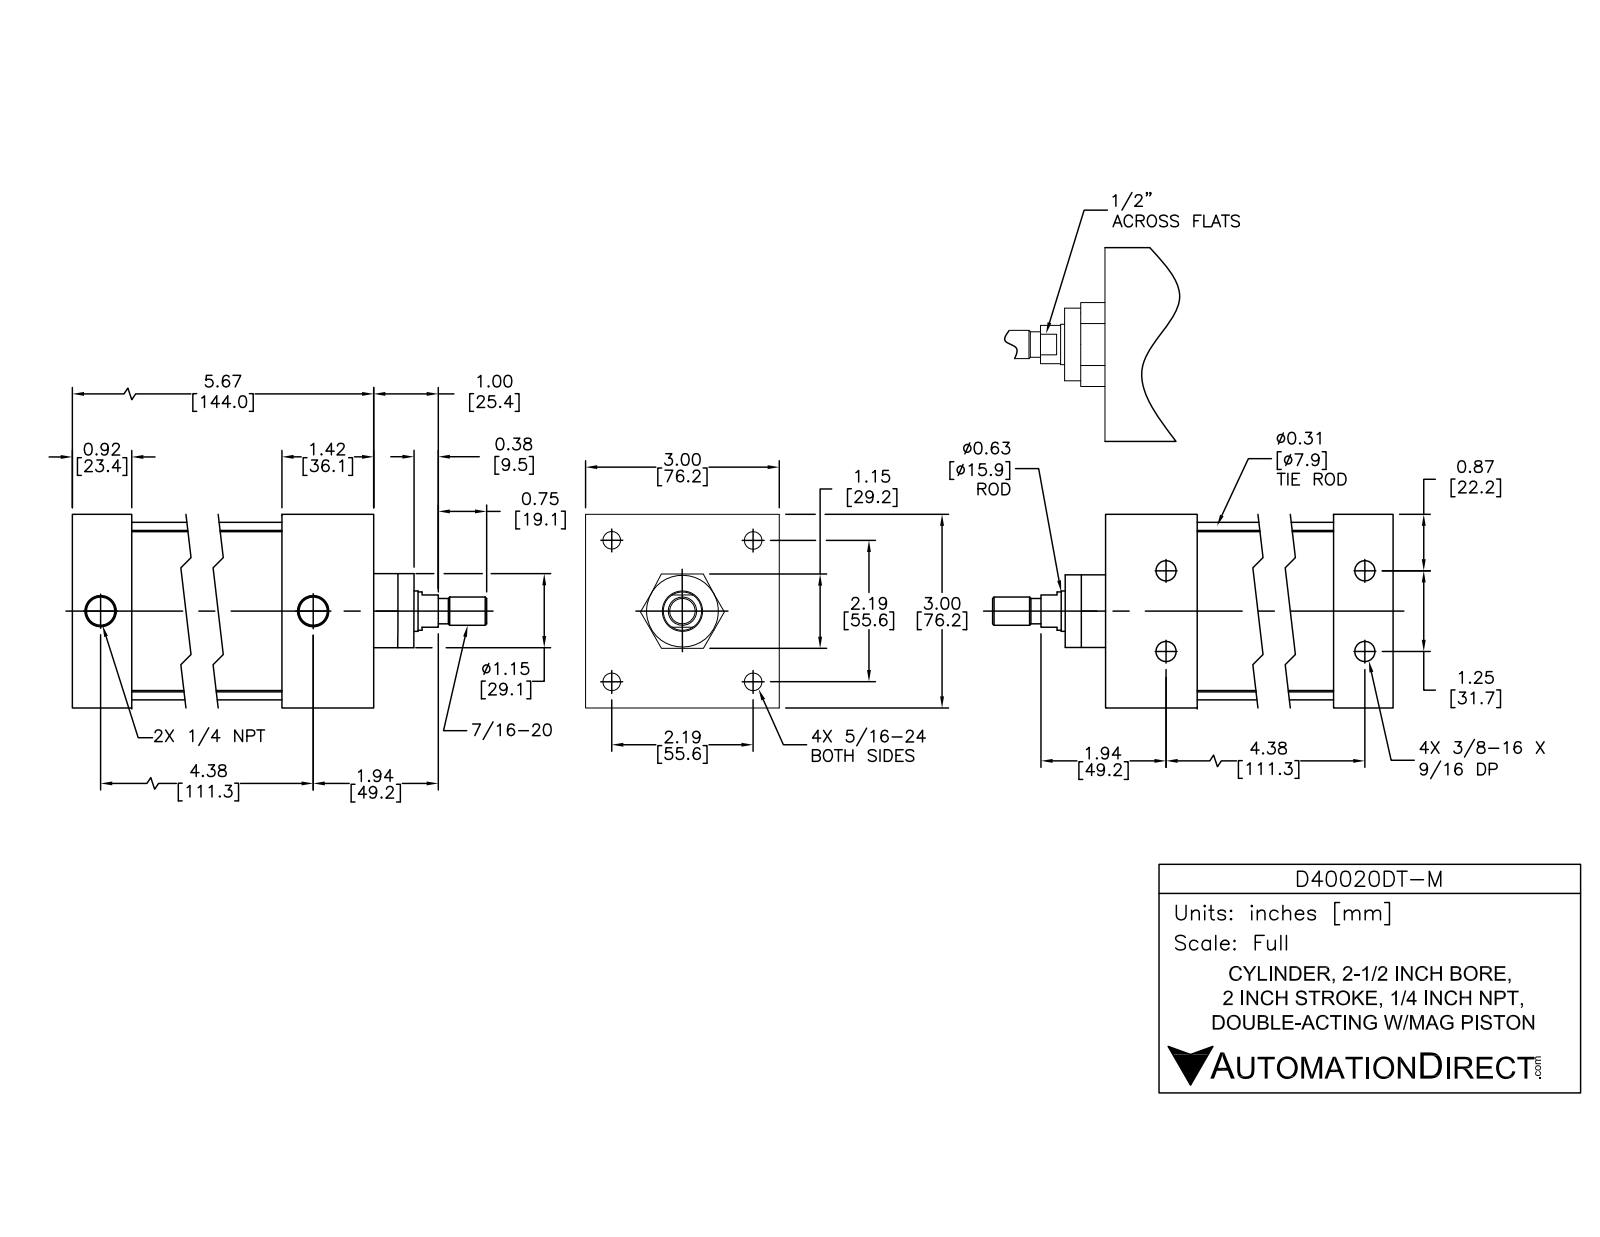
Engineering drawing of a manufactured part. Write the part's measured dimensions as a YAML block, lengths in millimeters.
part_name: "D40020DT-M; D40020DT-M BODY; D40020DT-M PISTON"
step_written_by: "SolidWorks 2015 (AUTOMOTIVE_DESIGN)"
units: millimeters
bodies: {solids: 12, faces: 298, planar: 94, cylindrical: 114, other: 90}
overall_size: [190.4, 76.2, 76.2]
volume: 530600
surface_area: 126900
round_holes:
  - {diameter: 6.8, count: 4}
  - {diameter: 7.8, count: 4}
  - {diameter: 9.1, count: 4}
  - {diameter: 12.7, count: 4}
  - {diameter: 7.5, count: 2}
  - {diameter: 12.1, count: 2}
  - {diameter: 15.9, count: 1}
  - {diameter: 16, count: 1}
  - {diameter: 63.5, count: 1}
round_bosses_or_shafts:
  - {diameter: 12.3, count: 4}
  - {diameter: 8, count: 4}
  - {diameter: 7.2, count: 4}
  - {diameter: 69.9, count: 1}
  - {diameter: 63.4, count: 1}
  - {diameter: 28.4, count: 1}
  - {diameter: 15.8, count: 1}
  - {diameter: 15, count: 1}
partial_cylinders:
  - {radius: 7.6, count: 4}
face_to_face_distances: [76.2, 2, 84.5, 145.9, 120, 25.9, 36.1, 84, 109.9, 25.4]
hole_center_spacings: [39.5, 55.9, 112.1, 111, 15.9, 15.9, 31.8, 79]
